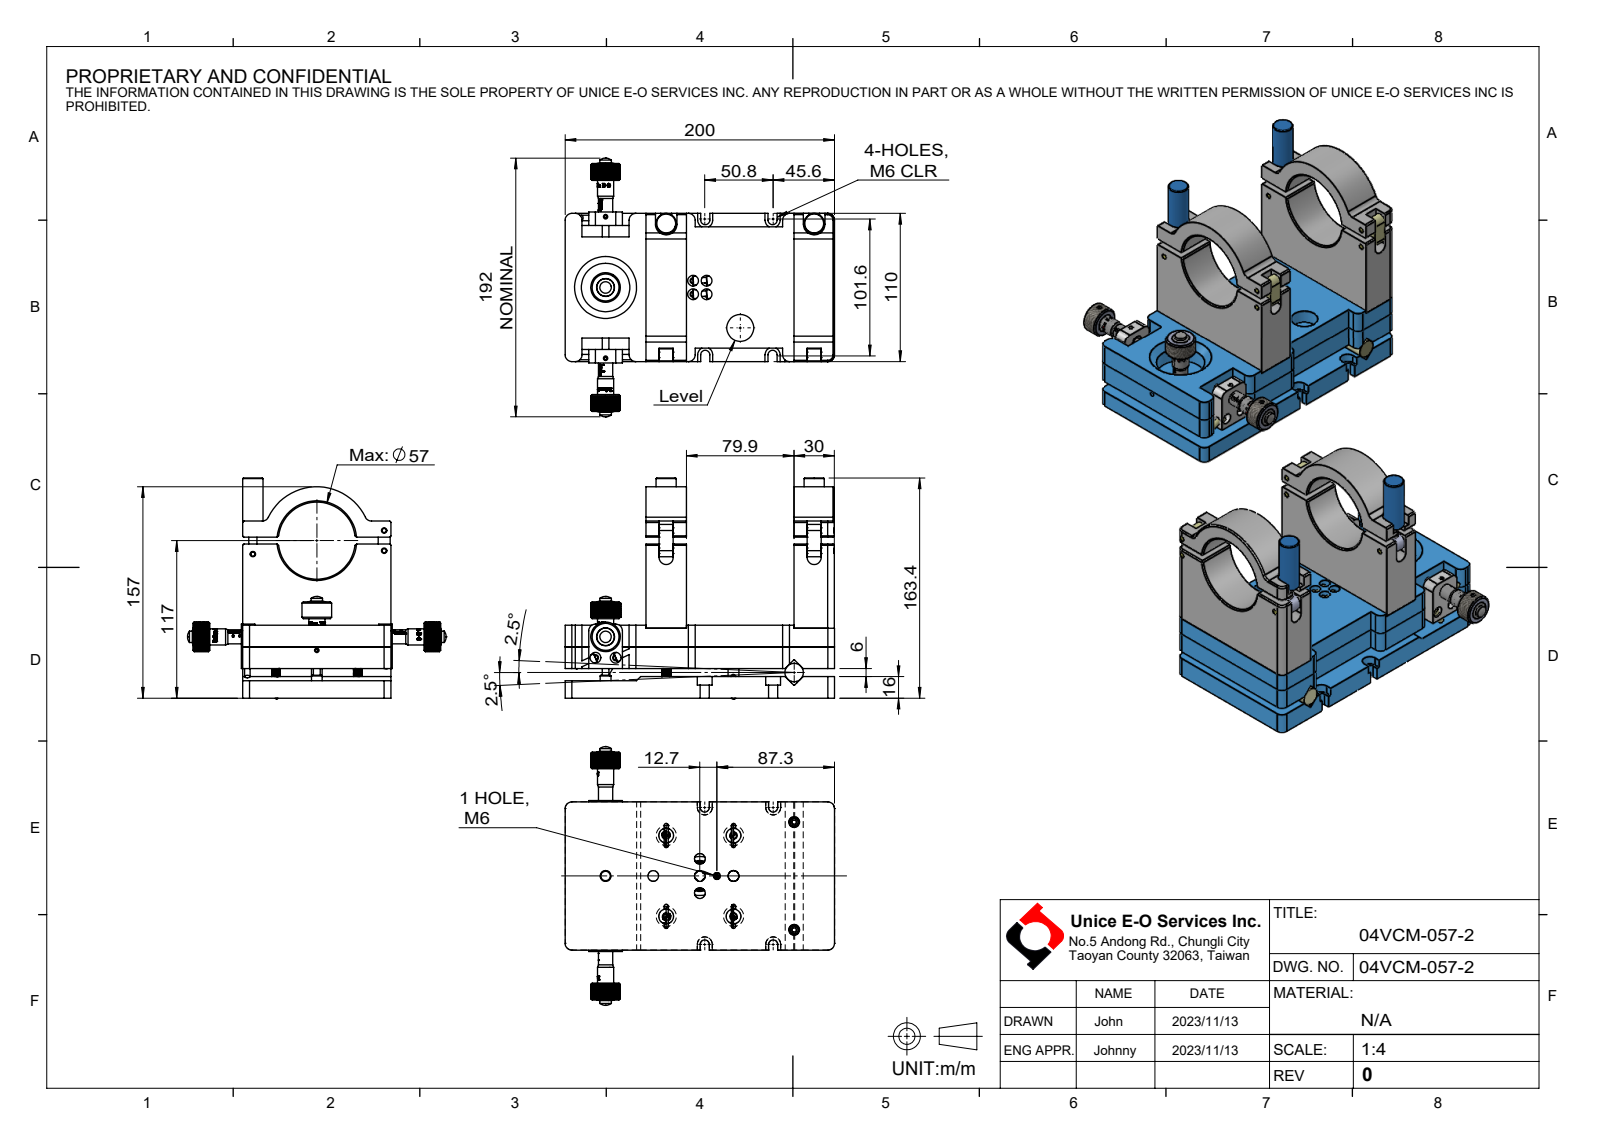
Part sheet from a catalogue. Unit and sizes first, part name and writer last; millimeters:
Units: millimetres
Overall size (bounding box): 200 × 192 × 164.25
Round holes (diameter × count): ⌀8 ×9, ⌀3.3 ×6, ⌀7.94 ×4, ⌀11 ×4, ⌀4 ×3, ⌀1.2 ×2, ⌀13.3 ×2, ⌀5.11 ×1, ⌀20 ×1, ⌀36 ×1, ⌀57.2 ×1
Round bosses / shafts (diameter × count): ⌀6.5 ×8, ⌀4 ×8, ⌀13 ×3, ⌀22 ×2, ⌀15 ×2, ⌀12 ×2, ⌀10.5 ×2, ⌀8.5 ×2
Partial cylindrical surfaces — rounded edges, fillets, slot ends (radius × count): R5 ×20, R1 ×9, R1.5 ×8, R3.38 ×4, R5.56 ×4, R0.5 ×2, R4.5 ×2, R5.25 ×2
Main face-to-face distances: 16, 22, 38.1, 16.1, 38, 30, 109.89, 6, 22.1, 110
Hole centre spacings: 39.05, 9.18, 18.39, 46.1, 7.07, 10, 30.4, 32.02
Bodies: 0 solids, 589 faces (296 planar, 227 cylindrical, 66 other)
Part name (STEP PRODUCT): 04VCM-057-2
STEP written by: SolidWorks 2022 (CONFIG_CONTROL_DESIGN)
